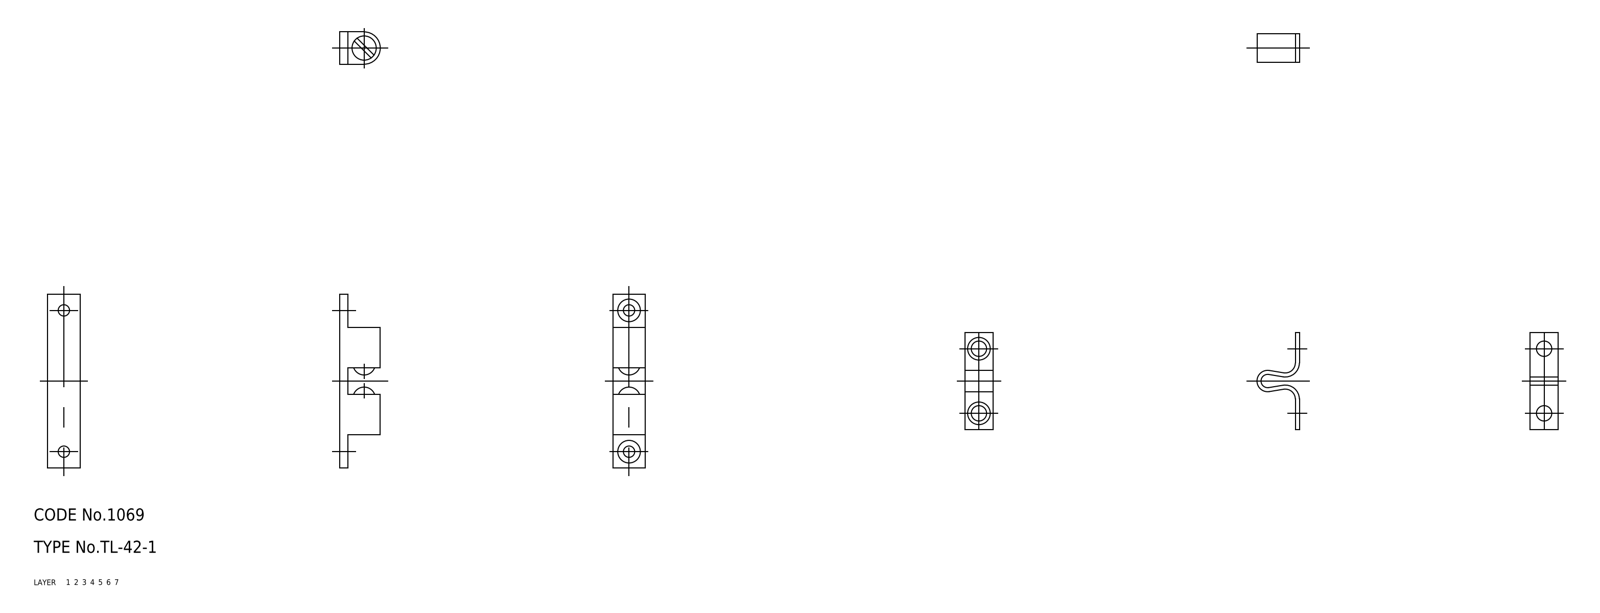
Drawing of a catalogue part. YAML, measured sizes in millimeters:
part_name: "ball; screw; keeper; housing (+1 more)"
step_written_by: "CADfix (AUTOMOTIVE_DESIGN)"
units: millimeters
bodies: {solids: 6, faces: 76, planar: 0, cylindrical: 0, other: 76}
overall_size: [43, 42.2, 8]
volume: 1933
surface_area: 2709
